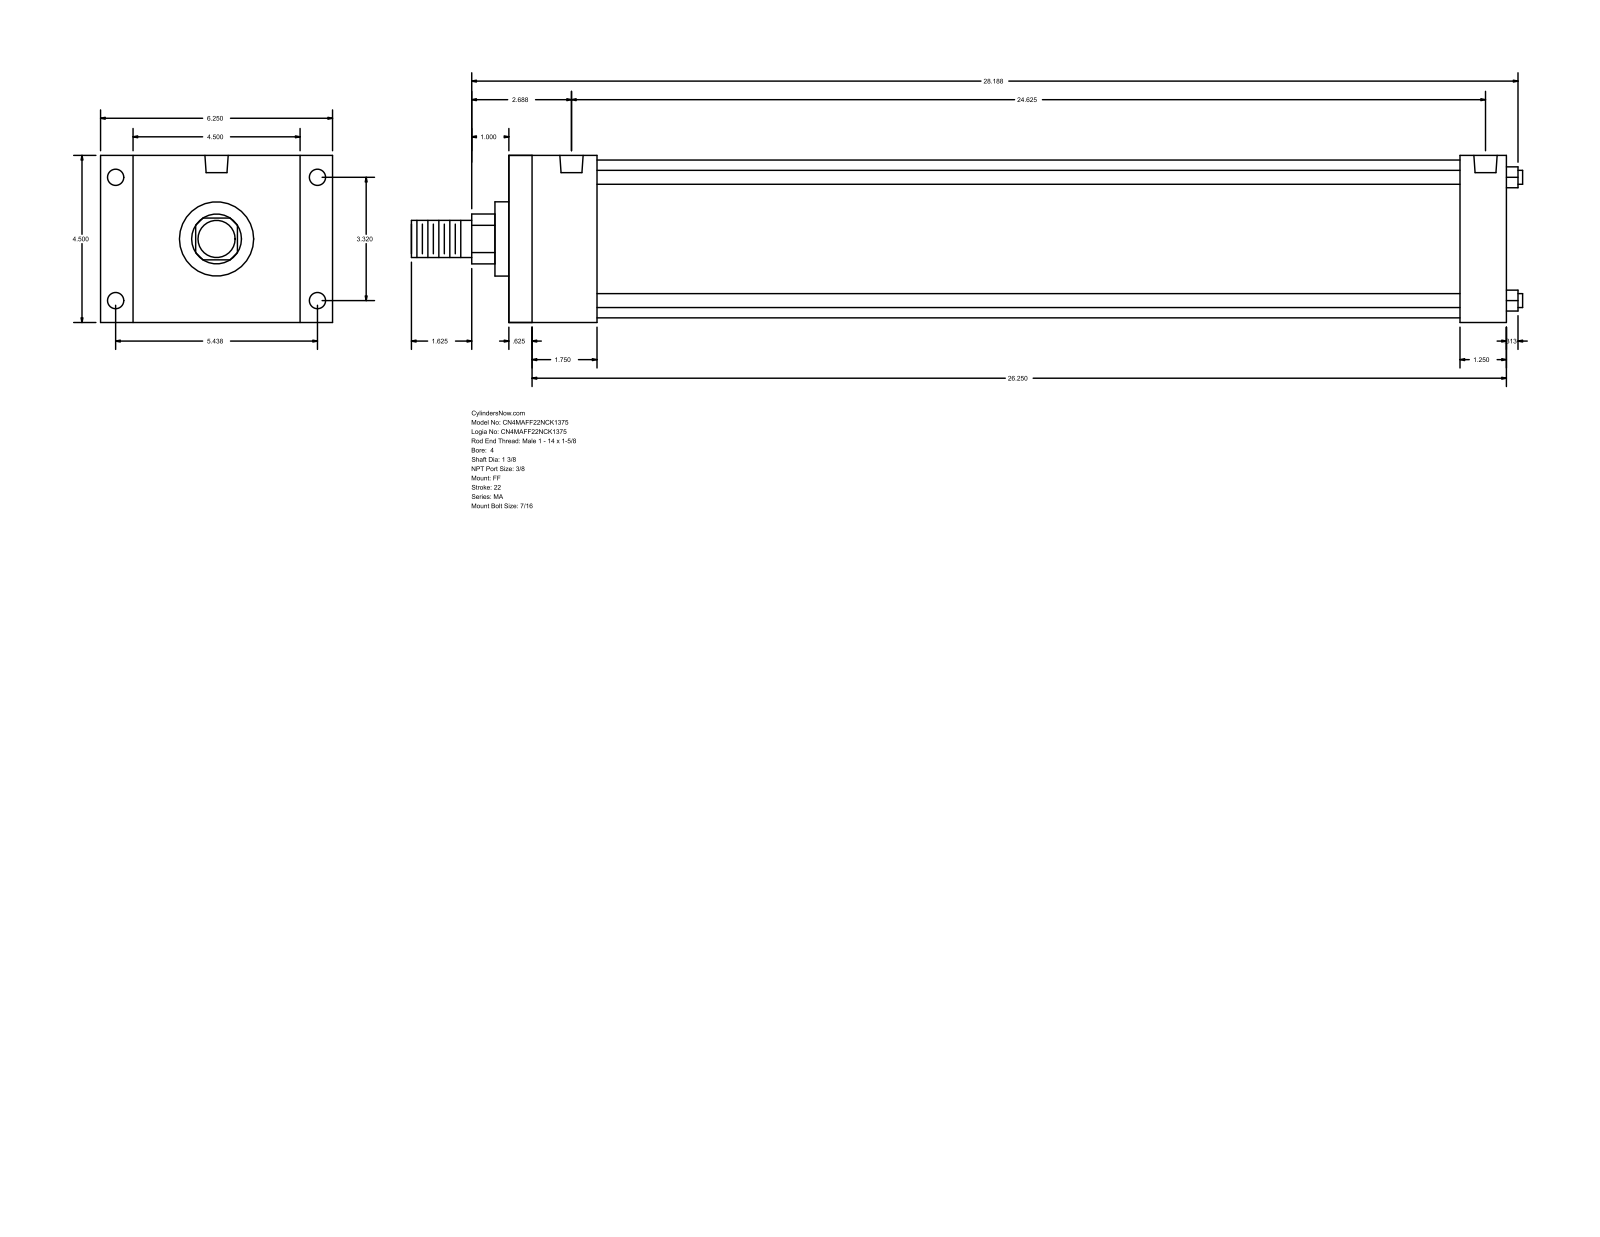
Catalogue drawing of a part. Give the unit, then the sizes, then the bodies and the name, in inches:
Units: inches
Overall size (bounding box): 29.937 × 6.25 × 4.5
Round holes (diameter × count): ⌀0.437 ×8, ⌀0.627 ×2
Round bosses / shafts (diameter × count): ⌀0.375 ×4, ⌀4.25 ×1, ⌀2 ×1, ⌀1.375 ×1, ⌀1 ×1
Partial cylindrical surfaces — rounded edges, fillets, slot ends (radius × count): R0.672 ×1
Main face-to-face distances: 4.5, 26.875, 0.625, 26.25, 0.875, 5.375, 25.625, 25, 1.25, 2.375
Hole centre spacings: 3.32, 5.438, 6.371, 24.25, 0.187, 0.188, 24.437, 24.438
Bodies: 0 solids, 92 faces (64 planar, 28 cylindrical, 0 other)
Part name (STEP PRODUCT): MA_FF__0400_1.375
STEP written by: GSSL Pune (CONFIG_CONTROL_DESIGN)
